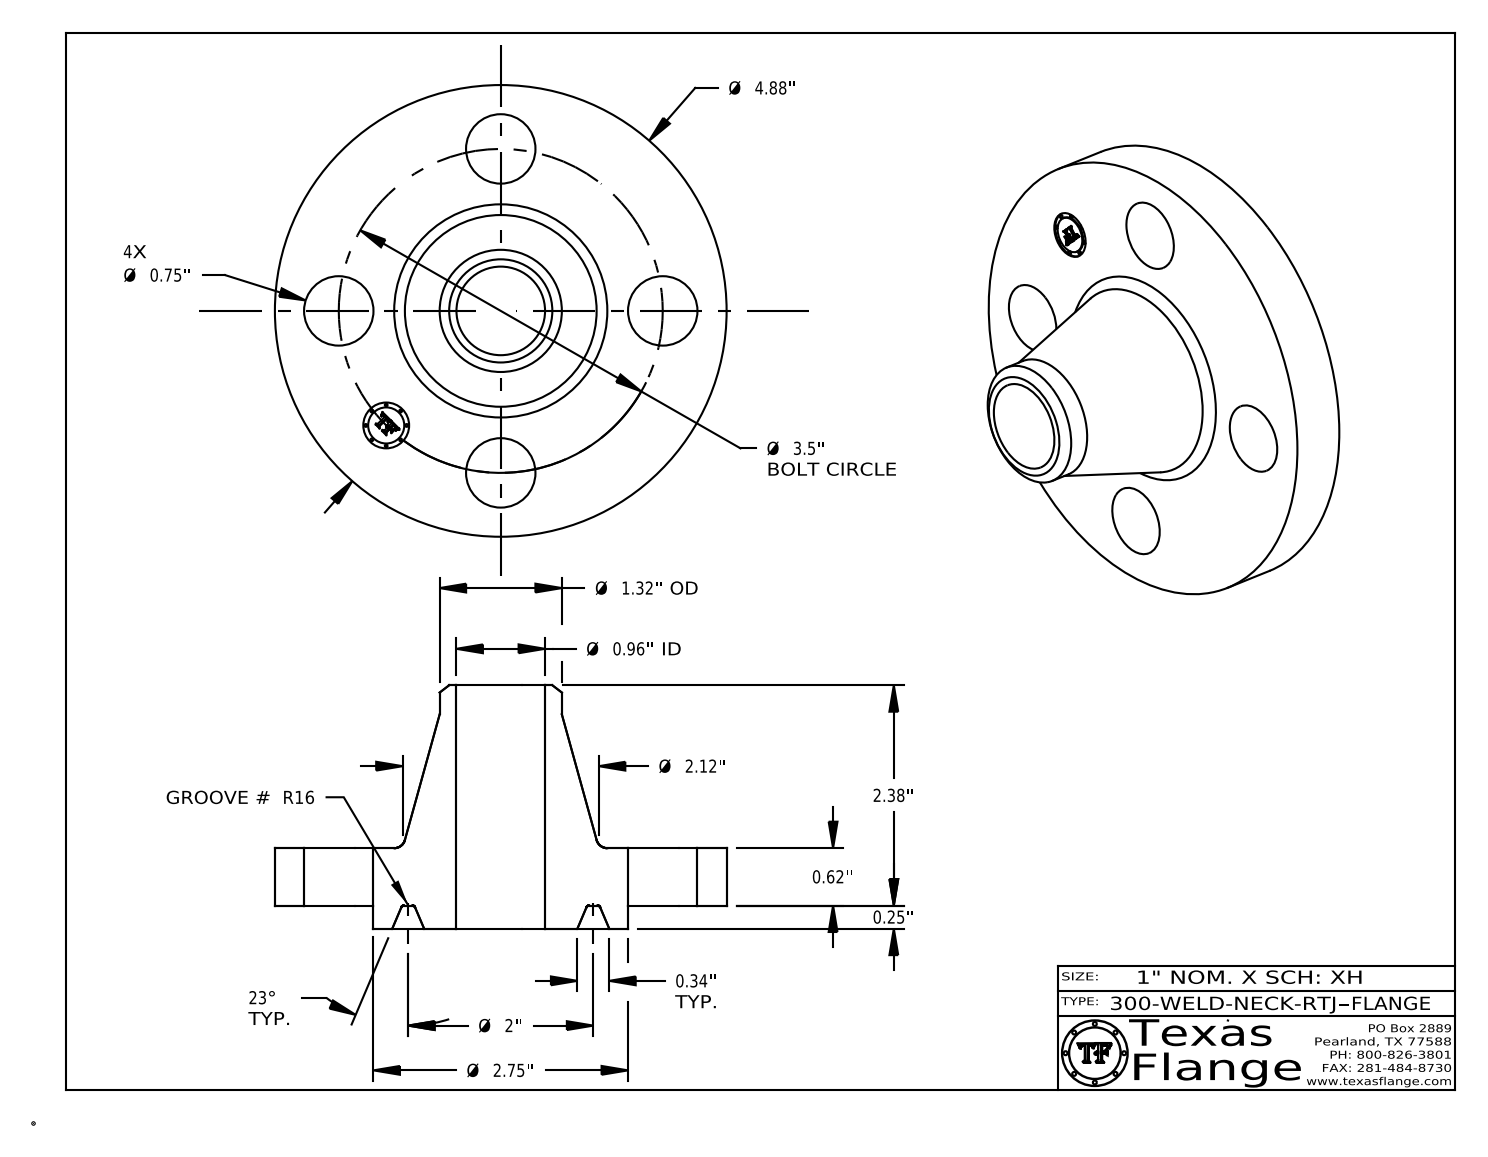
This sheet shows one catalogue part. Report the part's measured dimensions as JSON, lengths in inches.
{"part_name": "300-WELD-NECK-RTJ", "step_written_by": "CATIA V5 STEP AP214 (AUTOMOTIVE_DESIGN)", "units": "inches", "bodies": {"solids": 1, "faces": 421, "planar": 371, "cylindrical": 36, "other": 14}, "overall_size": [4.88, 4.88, 2.63], "volume_in3": 13.56, "surface_area_in2": 66.81, "round_holes": [[0.75, 4], [0.495, 1], [0.957, 1]], "round_bosses_or_shafts": [[0.03, 8], [4.88, 1], [2.75, 1], [1.32, 1], [0.39, 1]], "face_to_face_distances": [0.62, 0.25, 0.87, 2.63, 2.38, 1.76, 0.015, 0.855, 0.605, 1.775], "hole_center_spacings": [1.75, 2.475, 1.339, 3.233, 3.5]}
